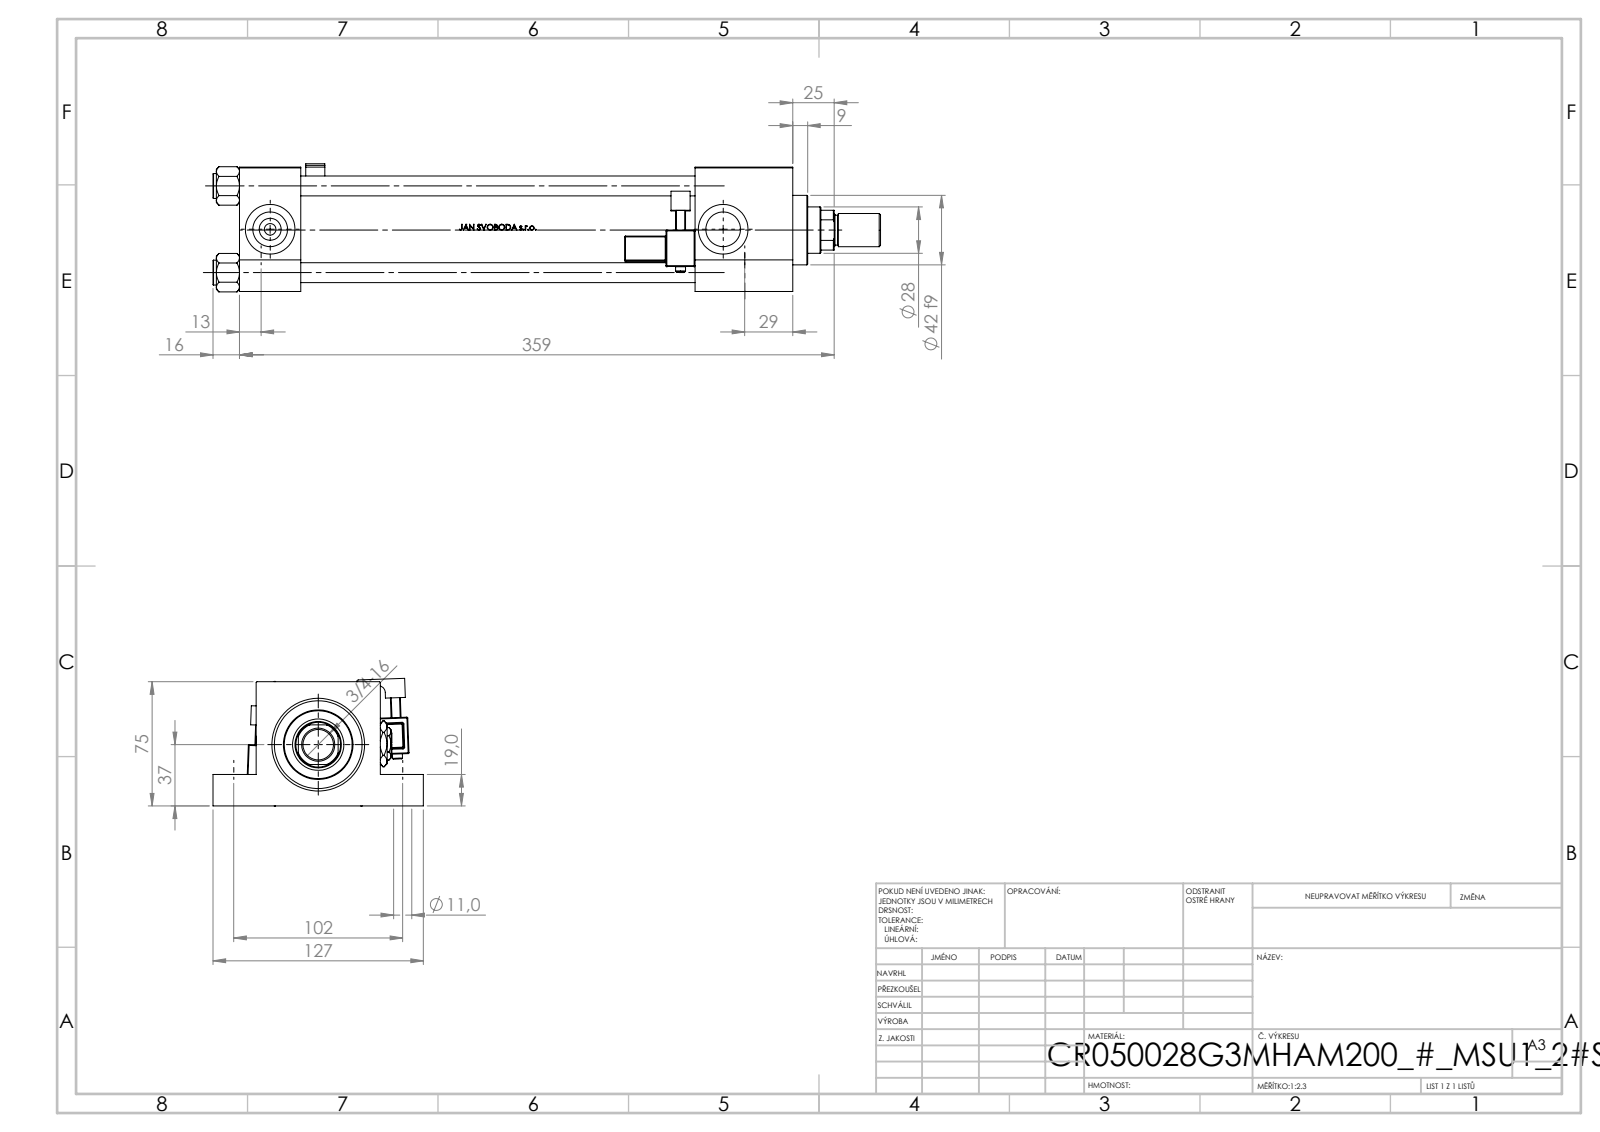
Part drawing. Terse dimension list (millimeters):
name: V215CR_G_Body; V215CR_MSU; NUT_M5_G; V215CR_VCP_G (+4 more)
written by: SolidWorks 2019 (CONFIG_CONTROL_DESIGN)
unit: mm
bodies: 16 solids, 1351 faces (539 planar, 196 cylindrical, 616 other)
size: 403 × 127 × 77.3
volume: 1 094 000 mm³; area: 285 184 mm²
holes: 4× ⌀11, 4× ⌀12, 2× ⌀7, 2× ⌀20.96, 2× ⌀30, 1× ⌀18.5, 1× ⌀28, 1× ⌀31, 1× ⌀41, 1× ⌀50, 1× ⌀53
bosses: 4× ⌀15, 2× ⌀6, 1× ⌀56, 1× ⌀42, 1× ⌀20, 1× ⌀18
rounds: 48× R0.5, 2× R1, 2× R2.5, 2× R4, 1× R6, 1× R13.5
face distances: 75, 37, 334, 297, 56, 19, 275, 238, 59, 26
hole spacings: 52.3, 36.63, 37.34, 73.96, 102, 292, 309.3, 273.5
